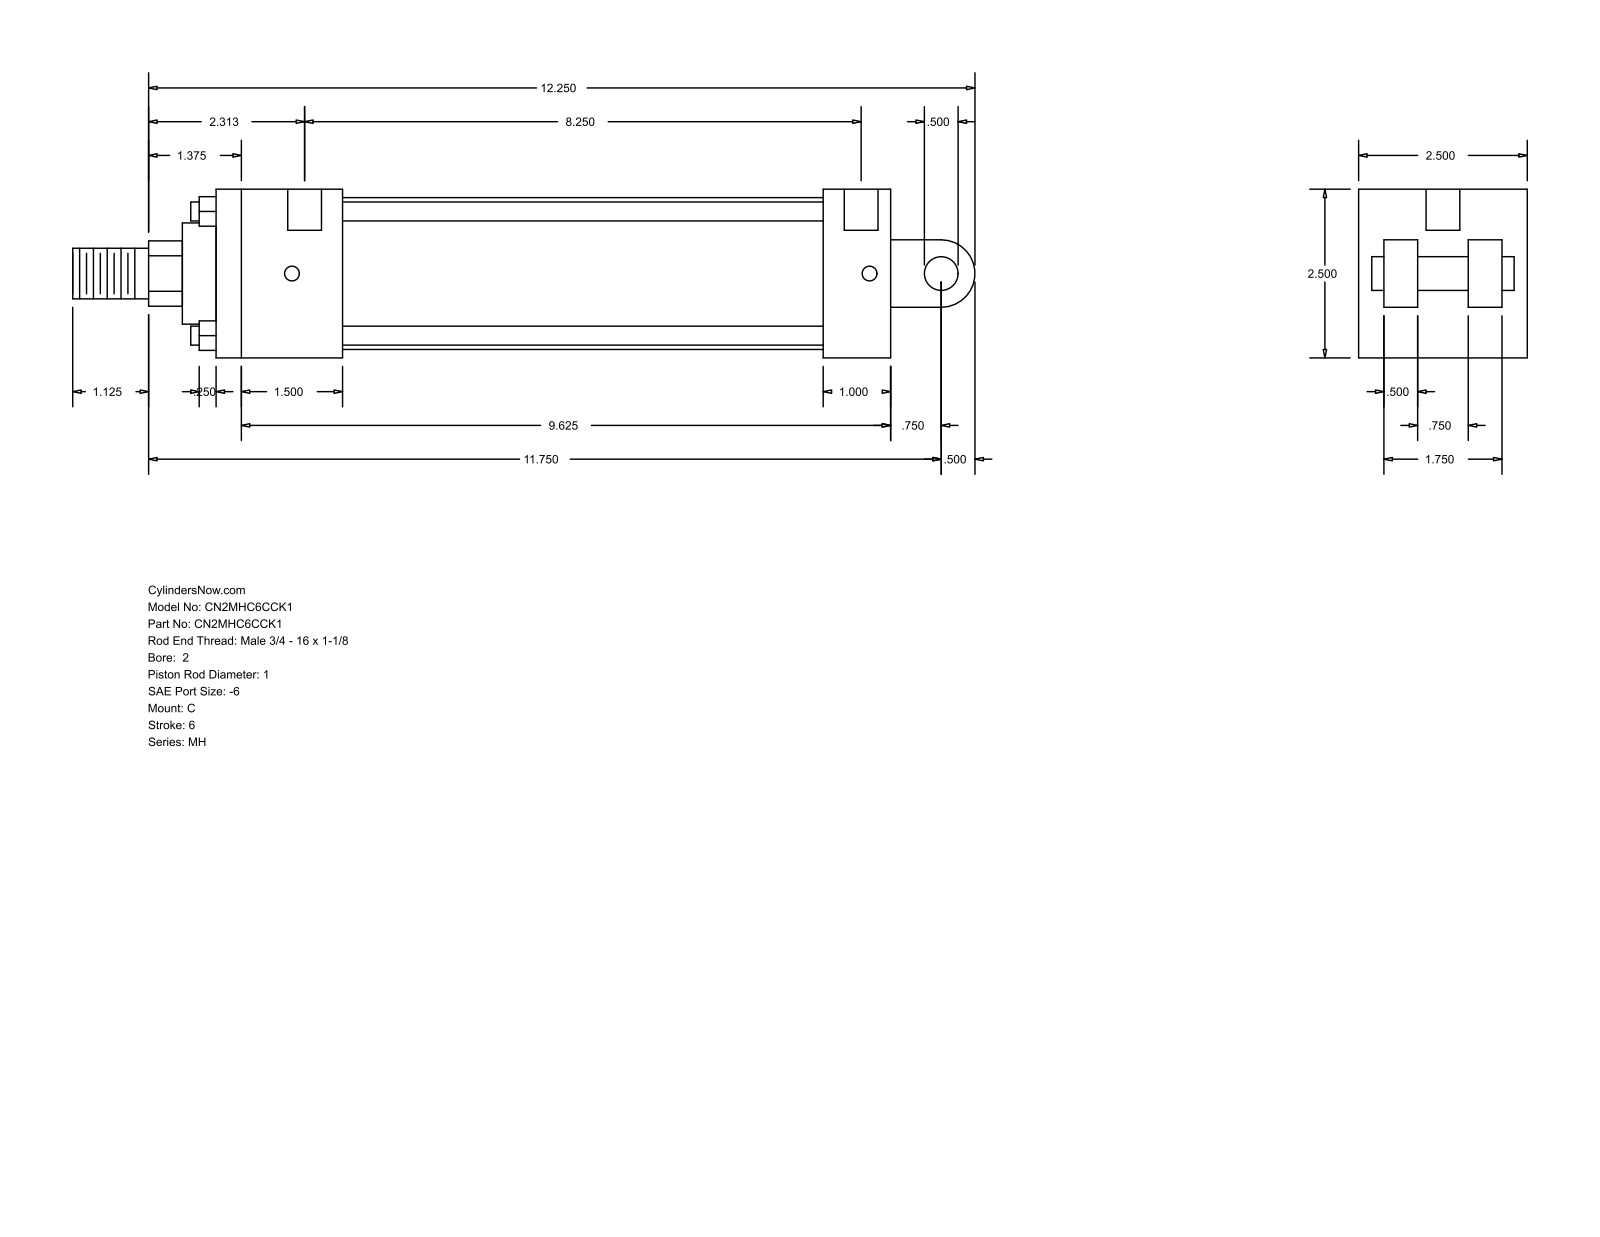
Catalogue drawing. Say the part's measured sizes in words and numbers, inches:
The part is named "MH_C__0200_1". Its 3-D file was written by "GSSL Pune (CONFIG_CONTROL_DESIGN)". It is 0 solids with 99 faces: 70 planar, 29 cylindrical and 0 other. Overall it measures 13.375 by 2.5 by 2.5 inches. Round holes: 4 of diameter 0.219, 2 of diameter 0.5. Round bosses or shafts: 4 of diameter 0.281, 1 of diameter 2.25, 1 of diameter 1.5, 1 of diameter 1, 1 of diameter 0.75, 1 of diameter 0.5. Partial cylindrical surfaces (rounded edges, fillets, slot ends): 1 of radius 0.484, 1 of radius 0.5. The main face-to-face distances are 2.5, 10, 0.5, 1, 1.875, 2.125, 0.375, 9, 7.125, 8.125. The hole center spacings are 8.562, 0.125, 0.187, 8.25, 8.375, 8.437.
